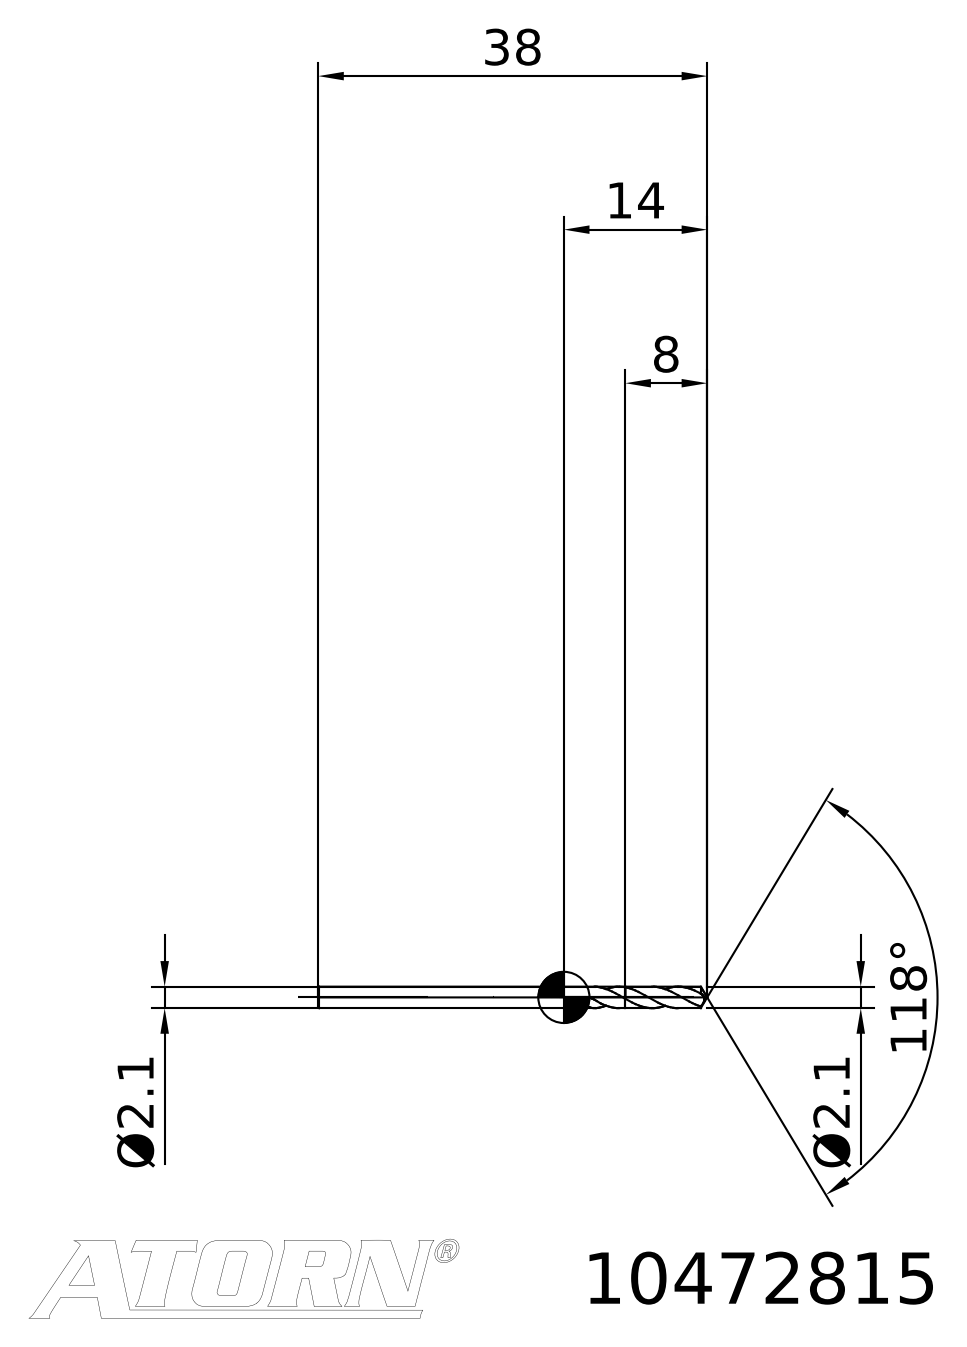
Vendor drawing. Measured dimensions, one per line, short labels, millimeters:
written by: TDM (AUTOMOTIVE_DESIGN)
unit: mm
bodies: 2 solids, 25 faces (3 planar, 0 cylindrical, 22 other)
size: 38 × 5.35 × 2.69
volume: 117 mm³; area: 264 mm²
face distances: 30
